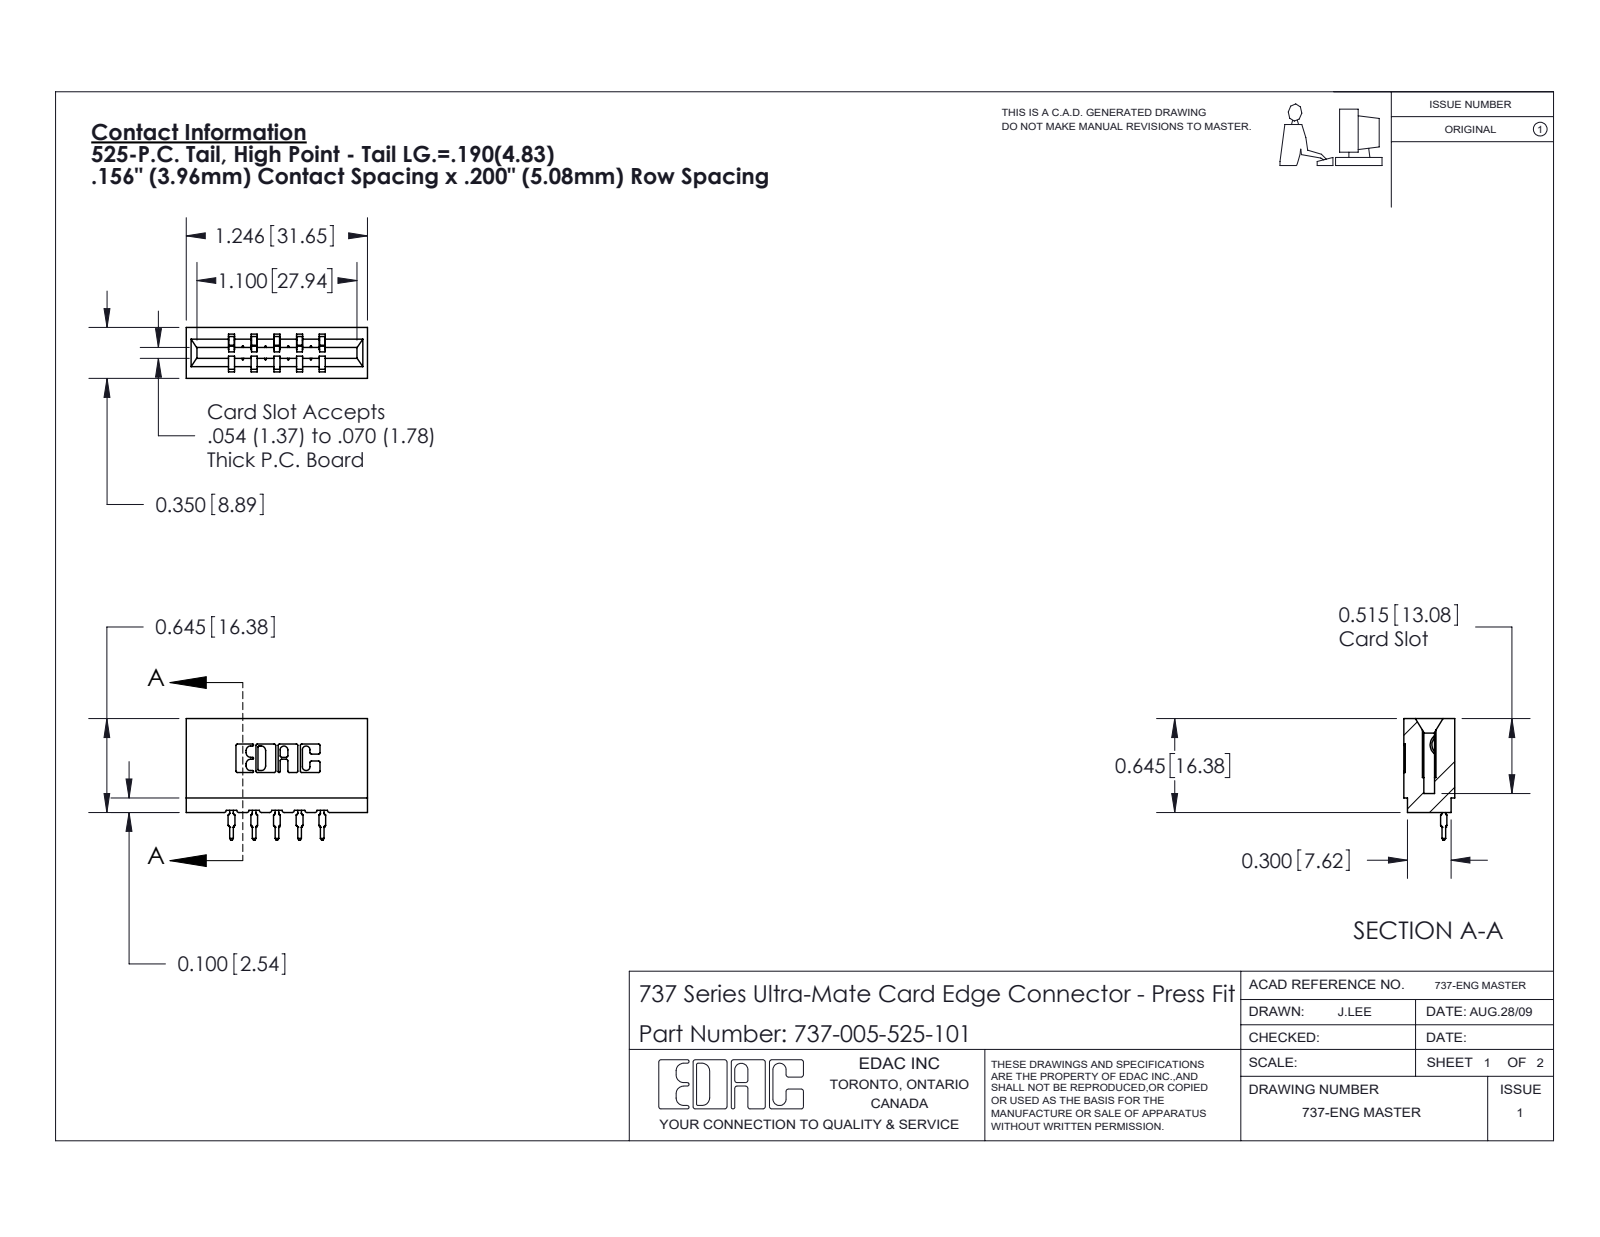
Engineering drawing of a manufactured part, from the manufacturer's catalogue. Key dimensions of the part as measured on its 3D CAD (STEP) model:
Part name (STEP PRODUCT): 737-005-525-101; 745-292-001_525; 737 Part_Insulator Option - 01
STEP written by: SolidWorks 2020 (CONFIG_CONTROL_DESIGN)
Units: inches
Bodies: 6 solids, 659 faces (394 planar, 135 cylindrical, 130 other)
Overall size (bounding box): 1.246 × 0.836 × 0.35
Volume: 0.202 in³ · Surface area: 5.815 in²
Partial cylindrical surfaces — rounded edges, fillets, slot ends (radius × count): R0.01 ×22, R0.015 ×10, R0.021 ×10, R0.007 ×6, R0.031 ×6, R0.005 ×4, R0.011 ×4, R0.026 ×3
Main face-to-face distances: 0.138, 0.212, 0.156, 0.35, 0.312, 0.198, 0.074, 0.354, 0.042, 0.025
